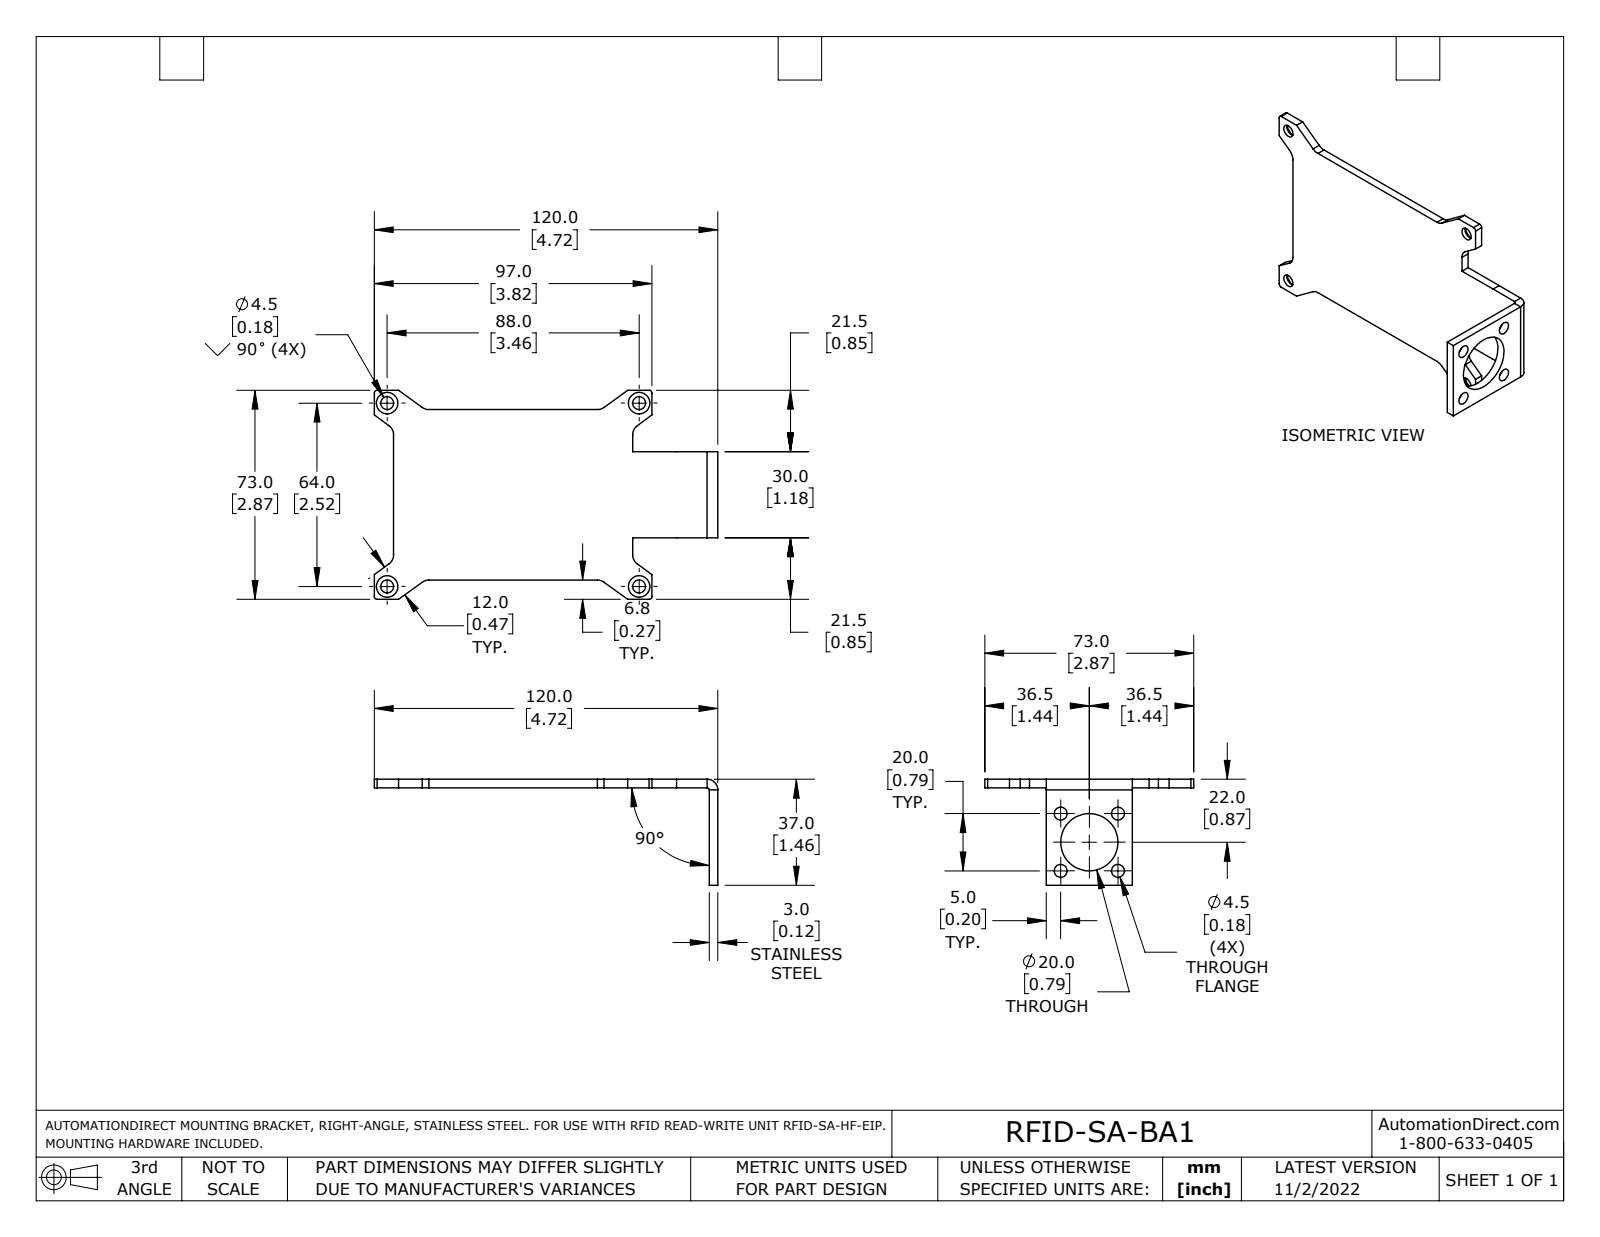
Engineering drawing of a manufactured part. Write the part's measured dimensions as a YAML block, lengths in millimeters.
part_name: "RFID-SA-BA1"
step_written_by: "SolidWorks 2021 (AUTOMOTIVE_DESIGN)"
units: millimeters
bodies: {solids: 1, faces: 61, planar: 34, cylindrical: 23, other: 4}
overall_size: [120, 73, 37]
volume: 20579
surface_area: 15715
round_holes:
  - {diameter: 4.5, count: 8}
  - {diameter: 20, count: 1}
partial_cylinders:
  - {radius: 4, count: 8}
  - {radius: 1, count: 4}
  - {radius: 0.74, count: 1}
  - {radius: 3.74, count: 1}
face_to_face_distances: [3, 14.75, 44.75, 30, 59.5, 6.75, 110.25, 113.25, 21.5, 51.5]
hole_center_spacings: [14.14, 20, 28.28, 64, 88, 108.81]
